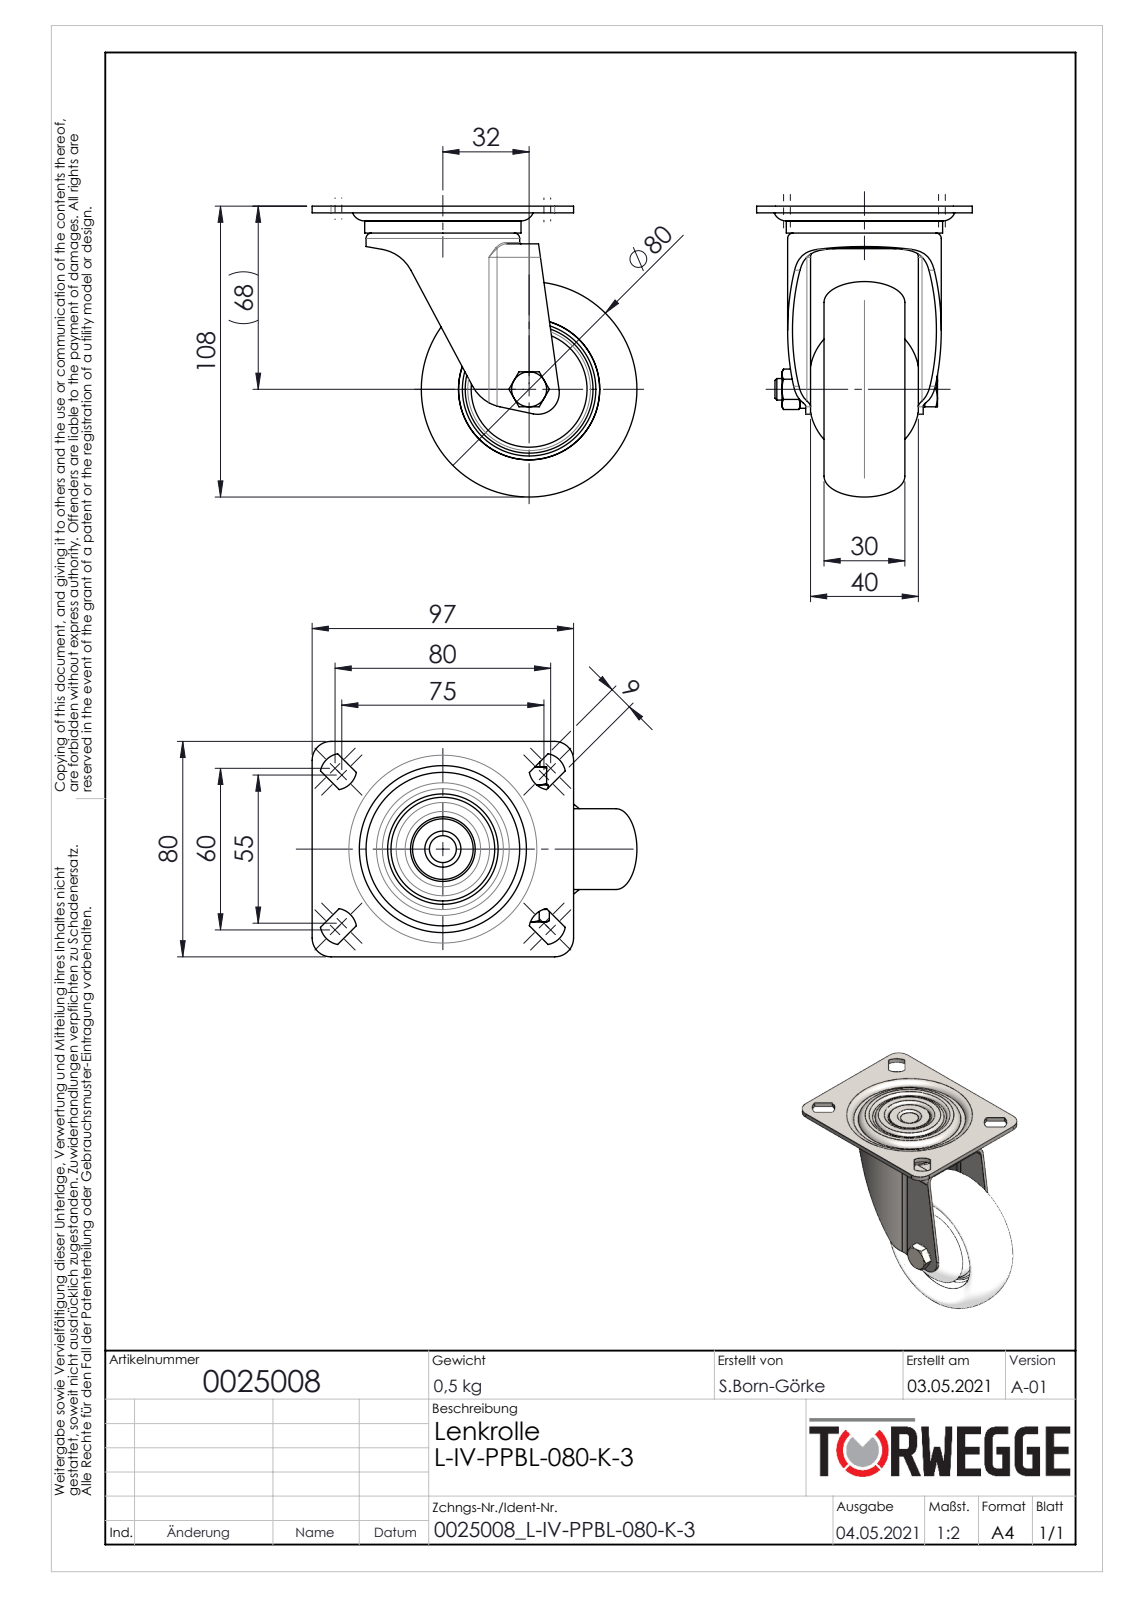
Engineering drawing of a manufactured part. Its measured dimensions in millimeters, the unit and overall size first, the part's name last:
Units: millimetres
Overall size (bounding box): 120.5 × 108 × 80
Round holes (diameter × count): ⌀6.8 ×1, ⌀8 ×1, ⌀8.1 ×1, ⌀8.3 ×1, ⌀10 ×1, ⌀24 ×1, ⌀29 ×1, ⌀33 ×1, ⌀35 ×1, ⌀53.4 ×1
Round bosses / shafts (diameter × count): ⌀58 ×1, ⌀57 ×1, ⌀22.5 ×1, ⌀21 ×1, ⌀15 ×1, ⌀14.1 ×1, ⌀13 ×1
Partial cylindrical surfaces — rounded edges, fillets, slot ends (radius × count): R8.07 ×8, R5 ×4, R7 ×4, R3.2 ×2, R6.8 ×2, R15 ×2, R8 ×1
Main face-to-face distances: 5.5, 2.5, 3, 1.8, 41.8, 6.3, 9.3, 11.8, 40, 10.05
Volume: 174 911 mm³ · Surface area: 90 121 mm²
Bodies: 10 solids, 316 faces (88 planar, 90 cylindrical, 138 other)
Part name (STEP PRODUCT): 0025008
STEP written by: SolidWorks 2020 (AUTOMOTIVE_DESIGN)
